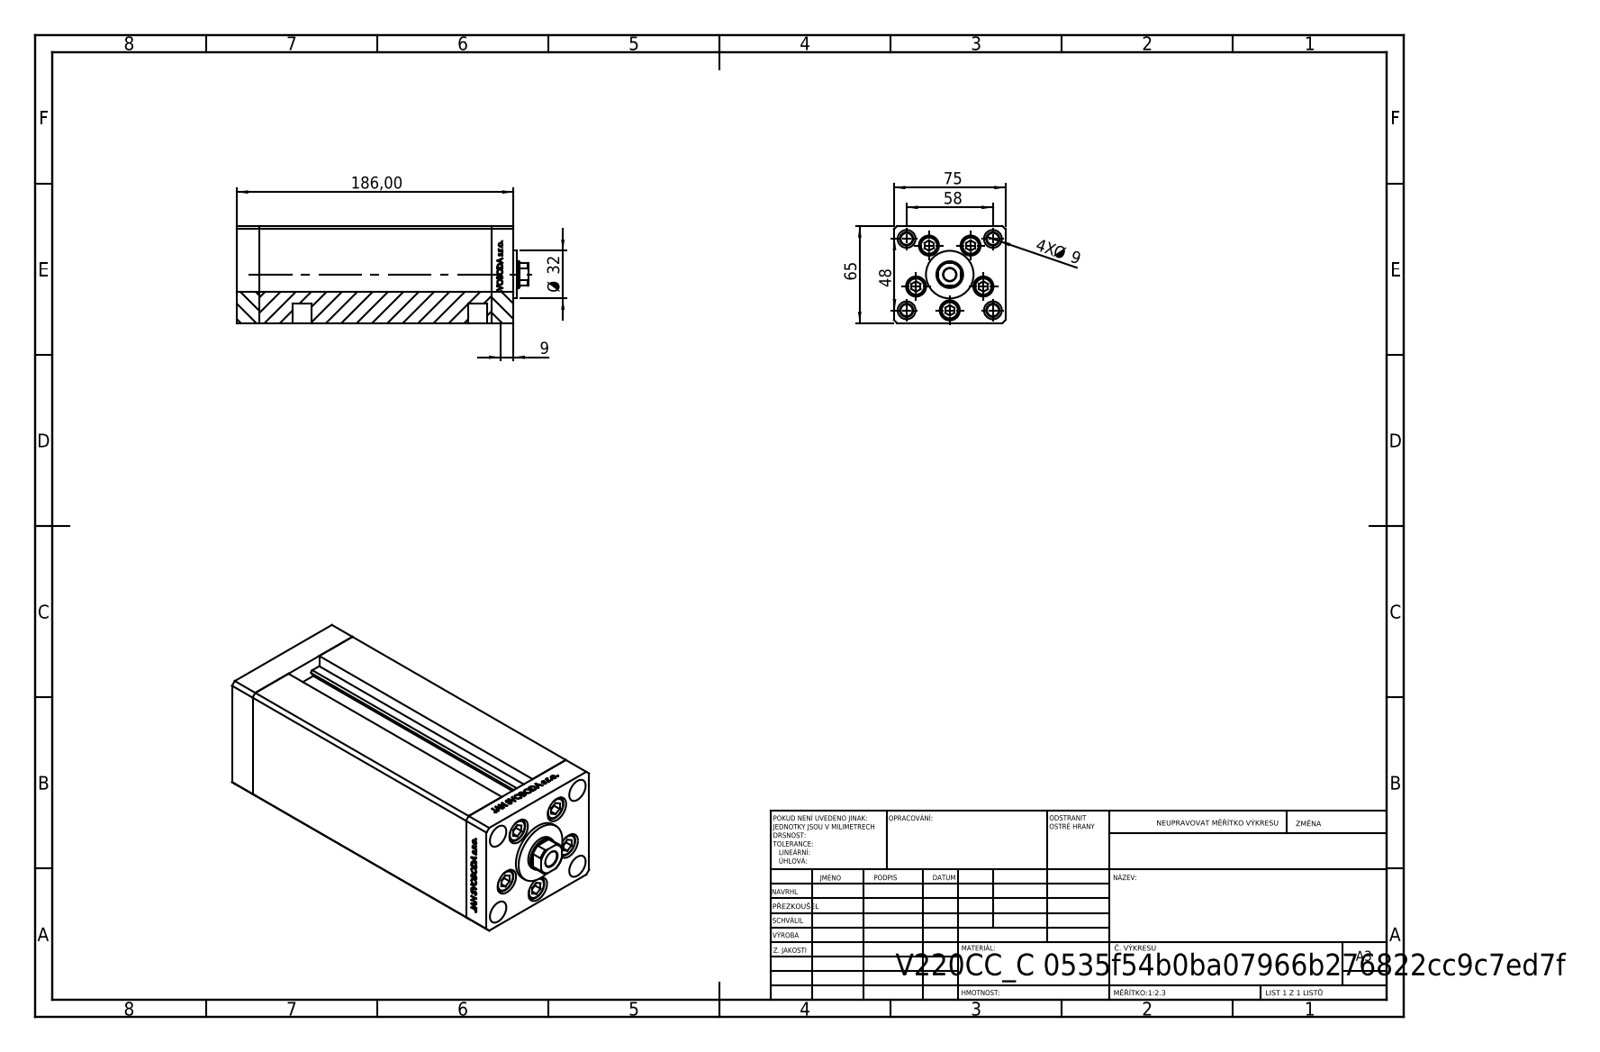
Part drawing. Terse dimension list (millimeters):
name: V220C BACK_C; V220C_VC_C; ALLEN BOLT; V220C_C MIDDLE (+1 more)
written by: SolidWorks 2019 (CONFIG_CONTROL_DESIGN)
unit: mm
bodies: 13 solids, 1179 faces (542 planar, 175 cylindrical, 462 other)
size: 196 × 75 × 65
volume: 754 279 mm³; area: 155 117 mm²
holes: 9× ⌀9, 5× ⌀13.5, 4× ⌀2, 4× ⌀8, 4× ⌀12, 4× ⌀13.16, 1× ⌀8.5, 1× ⌀12.5, 1× ⌀18
bosses: 5× ⌀8, 4× ⌀12.5, 1× ⌀32
rounds: 2× R0.93, 1× R8.5
face distances: 75, 65, 15, 156, 171, 186, 28, 13, 54.5, 10.5
hole spacings: 24, 37.64, 15.67, 17.22, 27.71, 28.83, 29, 32.63
